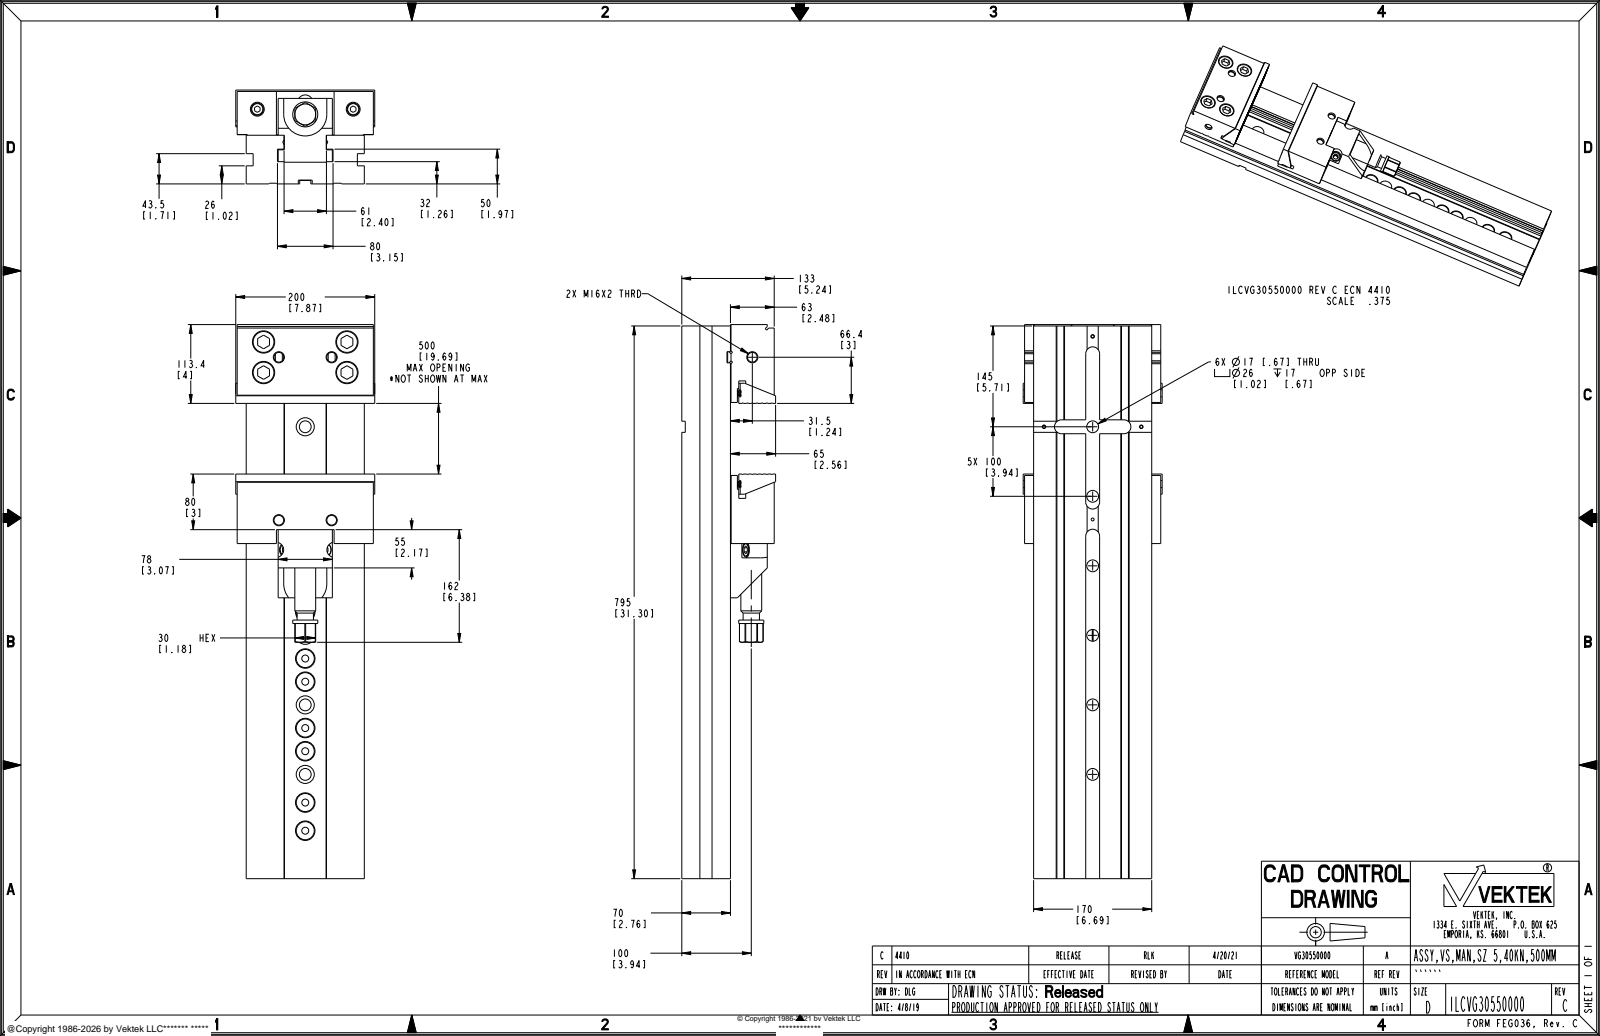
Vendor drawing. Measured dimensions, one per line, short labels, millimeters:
name: VG18050795; VG13550000; VG00112065; VG16550000 (+8 more)
written by: PRO/ENGINEER BY PARAMETRIC TECHNOLOGY CORPORATION, 2017170 (AUTOMOTIVE_DESIGN)
unit: mm
bodies: 22 solids, 930 faces (469 planar, 281 cylindrical, 180 other)
size: 797 × 200 × 135
volume: 9 878 000 mm³; area: 1 008 000 mm²
holes: 12× ⌀10, 8× ⌀14, 8× ⌀16, 7× ⌀17.5, 7× ⌀20, 6× ⌀17, 6× ⌀26, 4× ⌀4.2, 4× ⌀8.5, 4× ⌀9, 4× ⌀11.5, 4× ⌀22
bosses: 5× ⌀30, 4× ⌀16, 4× ⌀10, 2× ⌀15, 1× ⌀36, 1× ⌀24, 1× ⌀23.5, 1× ⌀20
rounds: 5× R10, 4× R5, 4× R8, 2× R2.1, 2× R11.5, 1× R11, 1× R13, 1× R17
face distances: 70, 38.8, 1, 10, 170, 38, 31.2, 44.5, 50, 45
hole spacings: 100, 33.3, 66.7, 200, 133.3, 166.7, 233.3, 266.7
